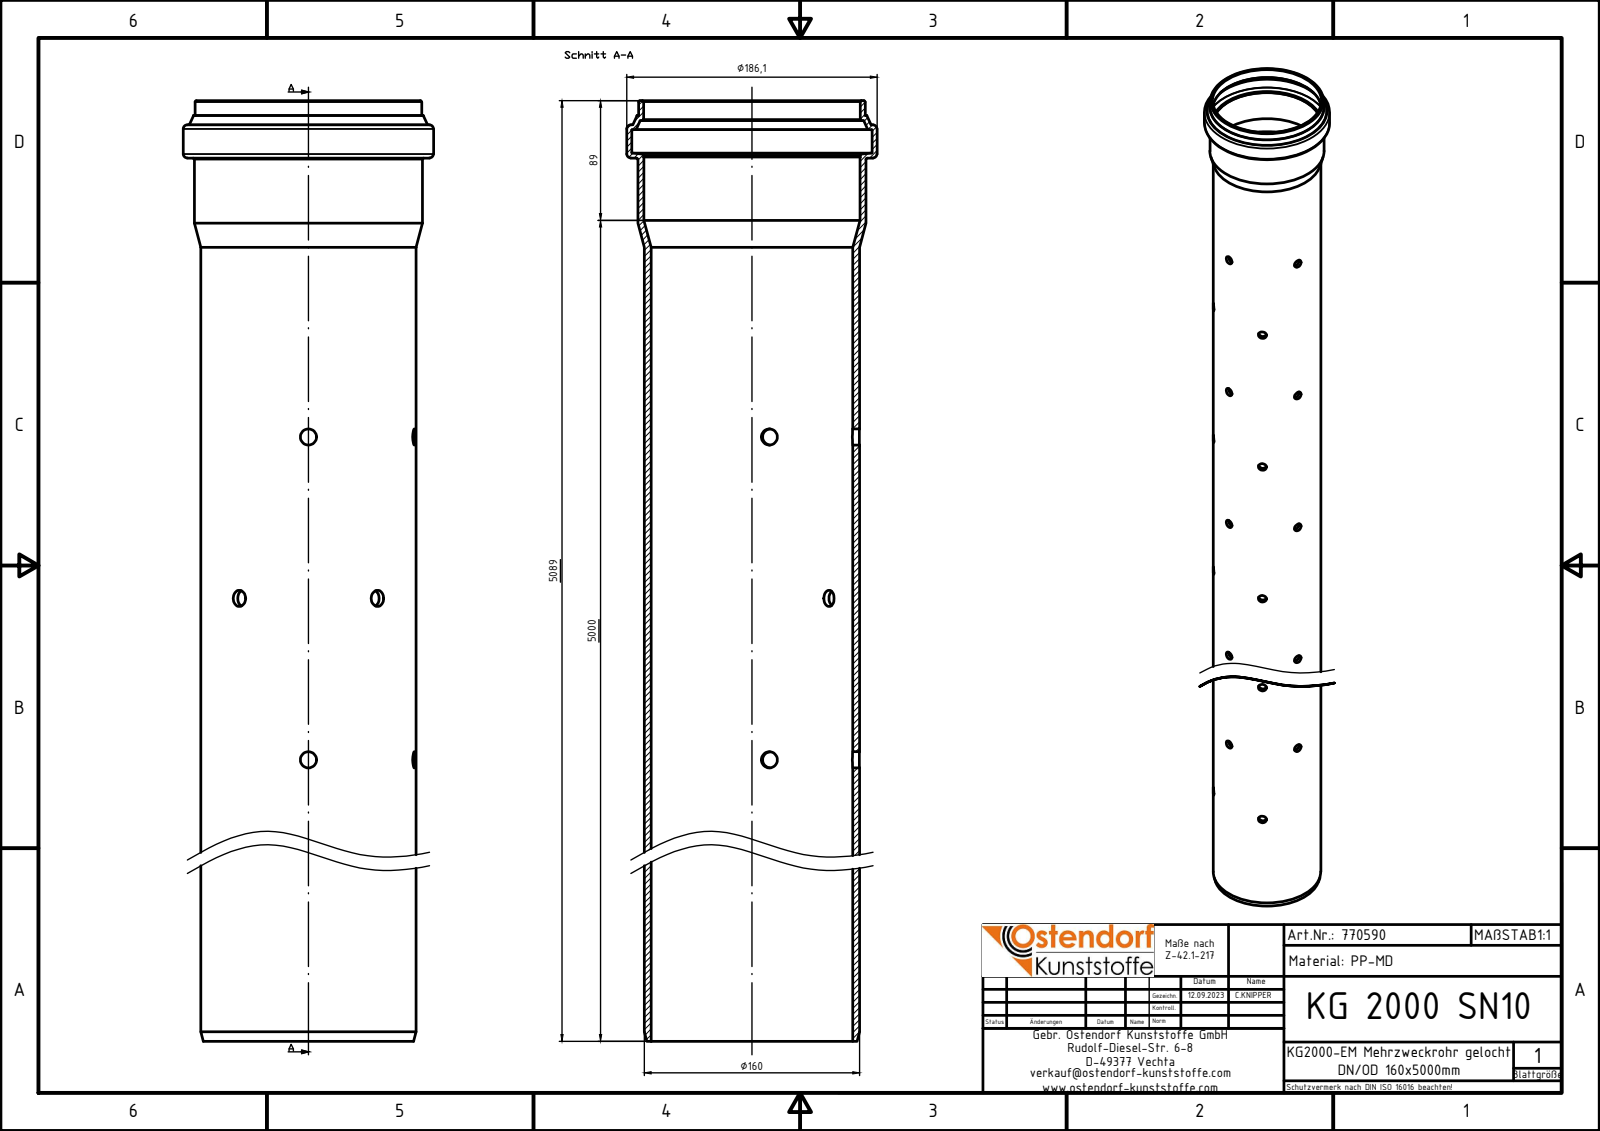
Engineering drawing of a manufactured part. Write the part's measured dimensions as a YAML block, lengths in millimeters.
part_name: "770590"
step_written_by: "Autodesk Inventor 2024 (AUTOMOTIVE_DESIGN)"
units: millimeters
bodies: {solids: 1, faces: 117, planar: 6, cylindrical: 89, other: 22}
overall_size: [5089, 186.1, 186.1]
volume: 12520000
surface_area: 4977000
round_holes:
  - {diameter: 12, count: 80}
  - {diameter: 149.85, count: 1}
  - {diameter: 160.6, count: 1}
  - {diameter: 161, count: 1}
  - {diameter: 178.7, count: 1}
round_bosses_or_shafts:
  - {diameter: 186.1, count: 1}
  - {diameter: 169.6, count: 1}
  - {diameter: 168.4, count: 1}
  - {diameter: 160, count: 1}
face_to_face_distances: [5046.3, 5089, 42.7, 5071, 24.7, 18, 5077.91, 31.61, 6.91, 11.09]
hole_center_spacings: [240, 480, 720, 960, 1200, 1440, 1680, 1920]
